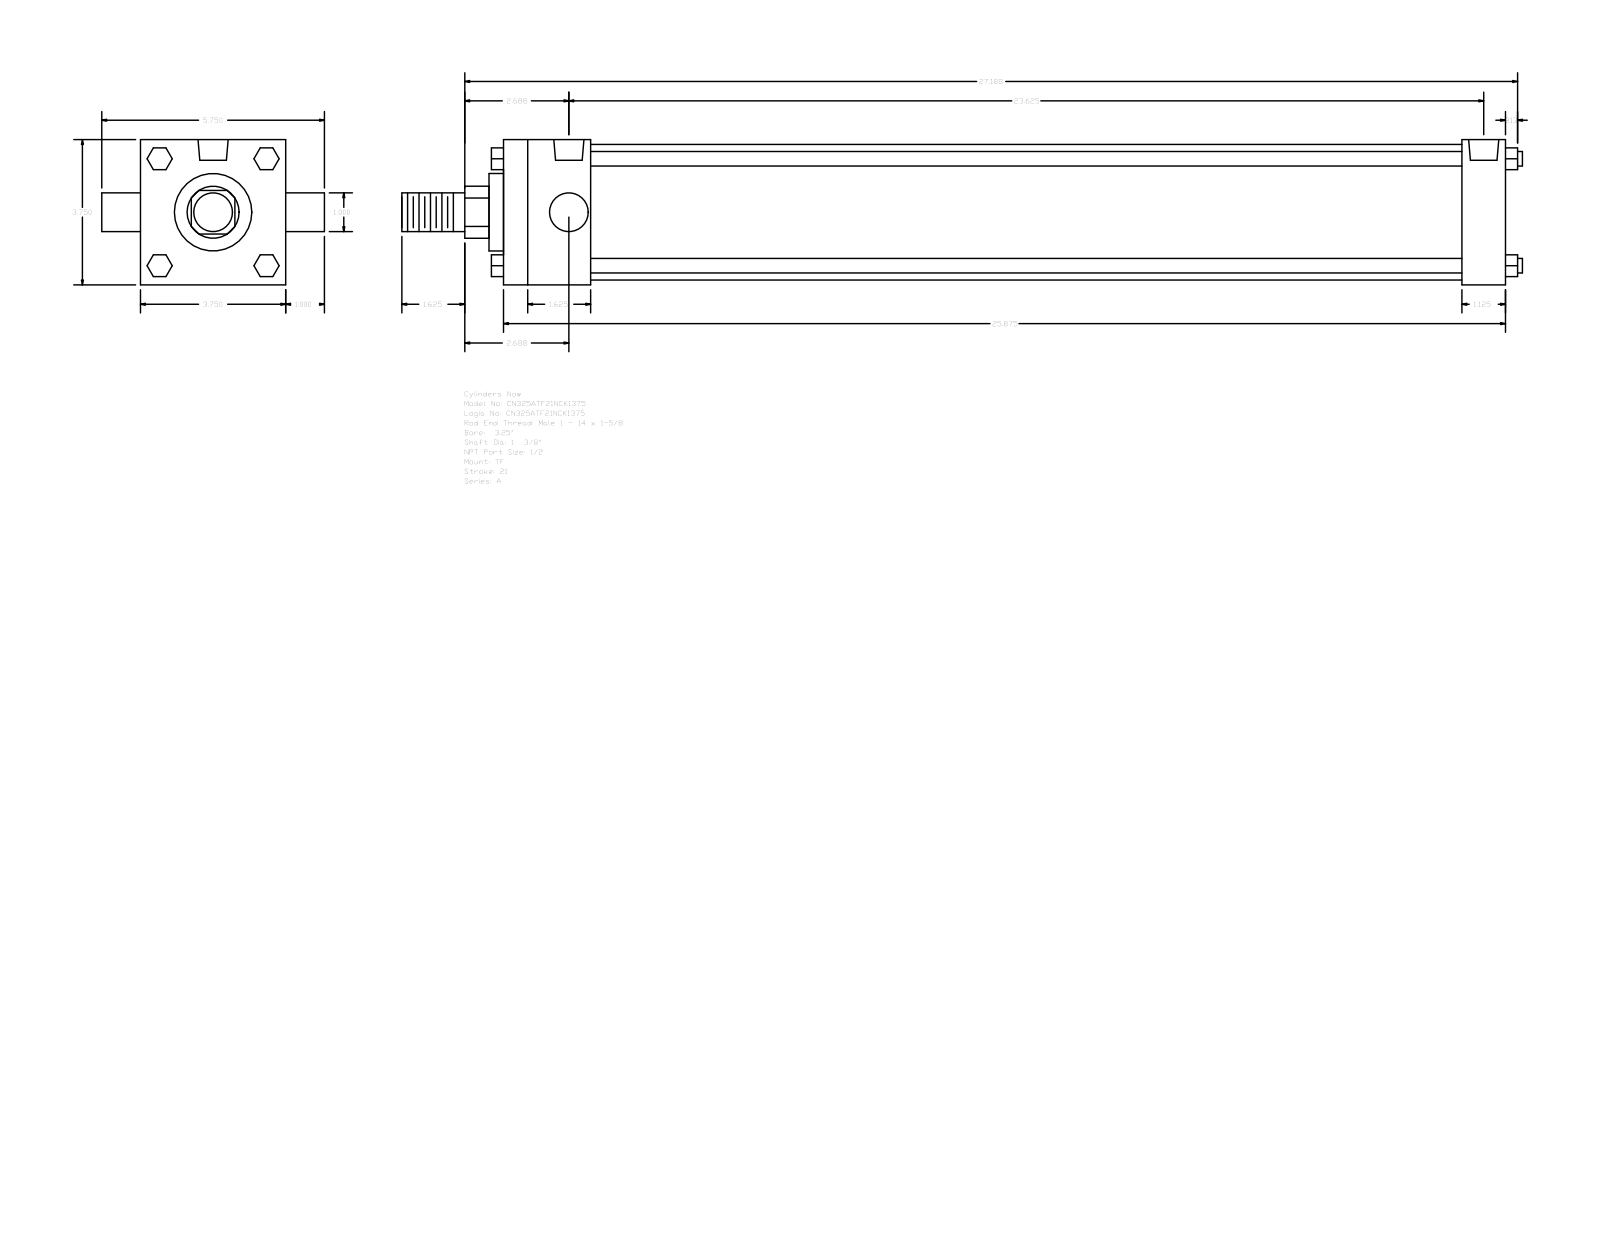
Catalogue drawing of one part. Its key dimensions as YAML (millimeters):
part_name: "A_TF__0325_1.375"
step_written_by: "GSSL Pune (CONFIG_CONTROL_DESIGN)"
units: millimeters
bodies: {solids: 0, faces: 120, planar: 92, cylindrical: 28, other: 0}
overall_size: [735.01, 146.05, 95.25]
round_holes:
  - {diameter: 8.73, count: 3}
  - {diameter: 19.77, count: 2}
round_bosses_or_shafts:
  - {diameter: 9.53, count: 4}
  - {diameter: 25.4, count: 2}
  - {diameter: 88.9, count: 1}
  - {diameter: 50.8, count: 1}
  - {diameter: 34.92, count: 1}
partial_cylinders:
  - {radius: 17.06, count: 1}
face_to_face_distances: [95.24, 657.22, 57.15, 628.65, 571.5, 600.07, 28.57, 66.67, 9.52, 638.17]
hole_center_spacings: [3.18, 596.9, 593.72, 600.08]
